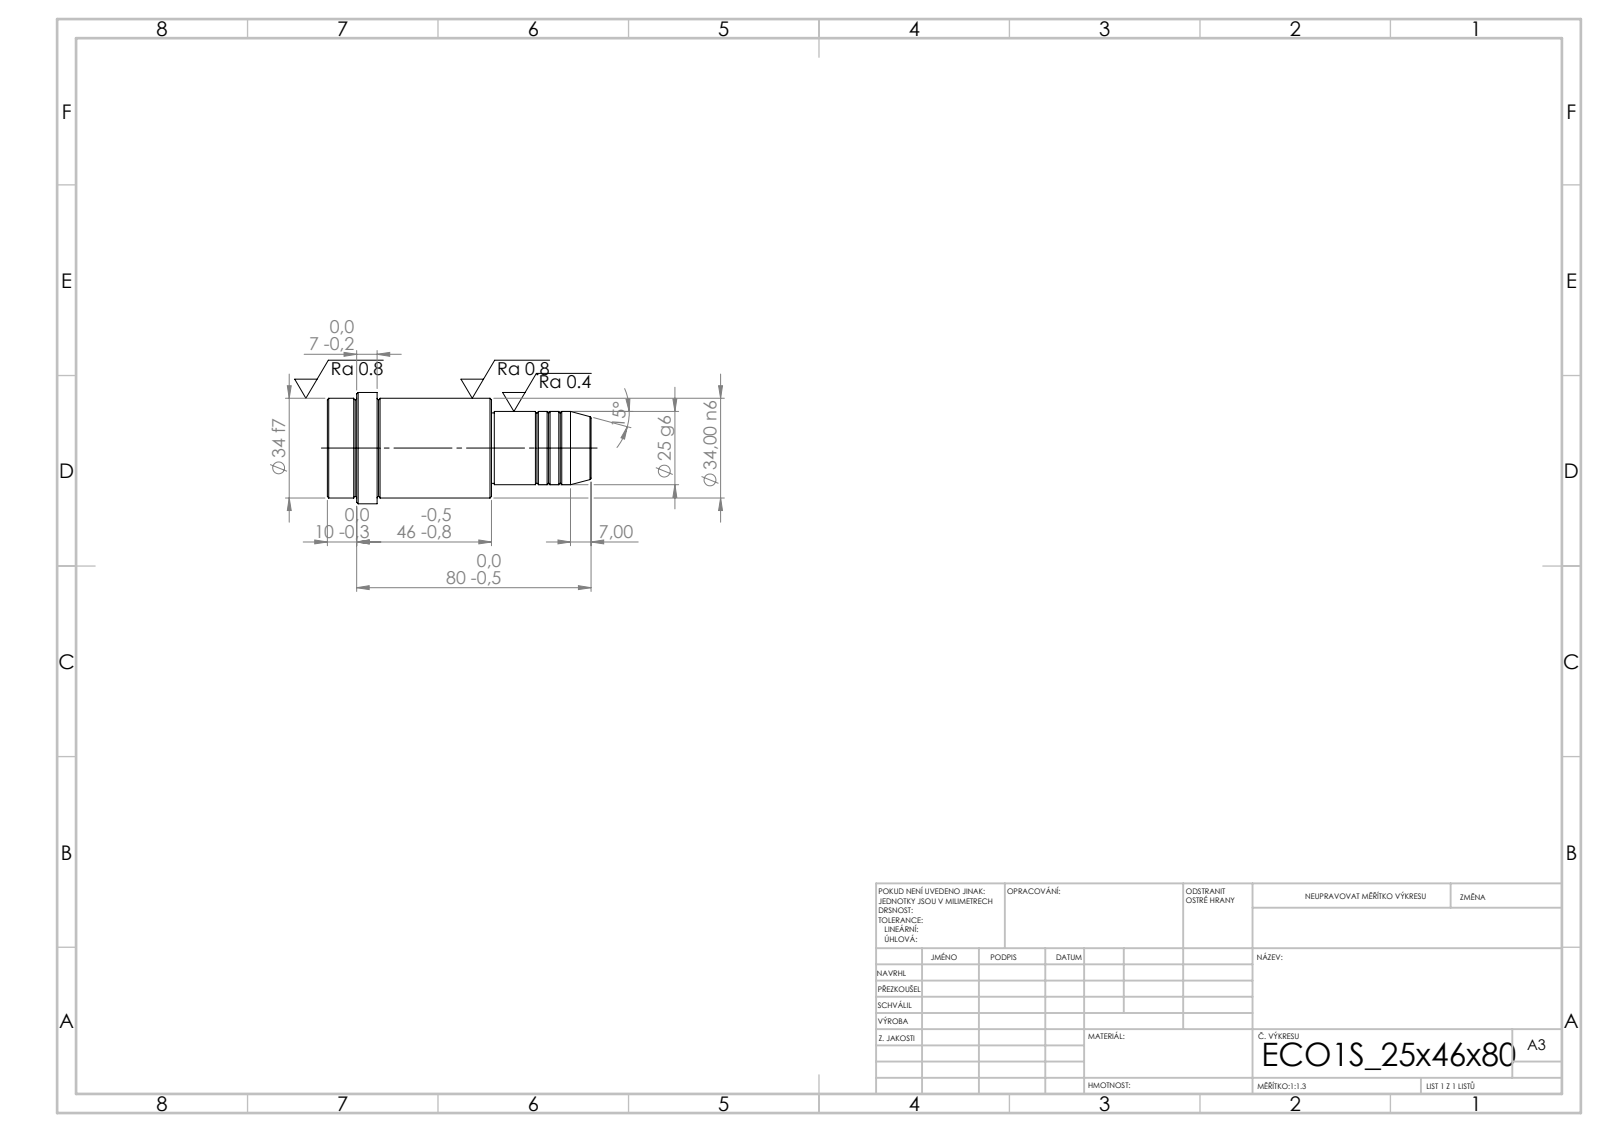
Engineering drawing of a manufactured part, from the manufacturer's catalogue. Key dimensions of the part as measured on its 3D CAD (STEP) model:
STEP written by: SolidWorks 2019 (CONFIG_CONTROL_DESIGN)
Units: millimetres
Bodies: 1 solid, 52 faces (6 planar, 16 cylindrical, 30 other)
Overall size (bounding box): 90 × 38 × 38
Volume: 68 371 mm³ · Surface area: 11 057 mm²
Round bosses / shafts (diameter × count): ⌀38 ×1, ⌀34 ×1, ⌀25 ×1, ⌀24 ×1
Main face-to-face distances: 56, 34, 90, 73, 39, 17, 80, 46, 7, 10
